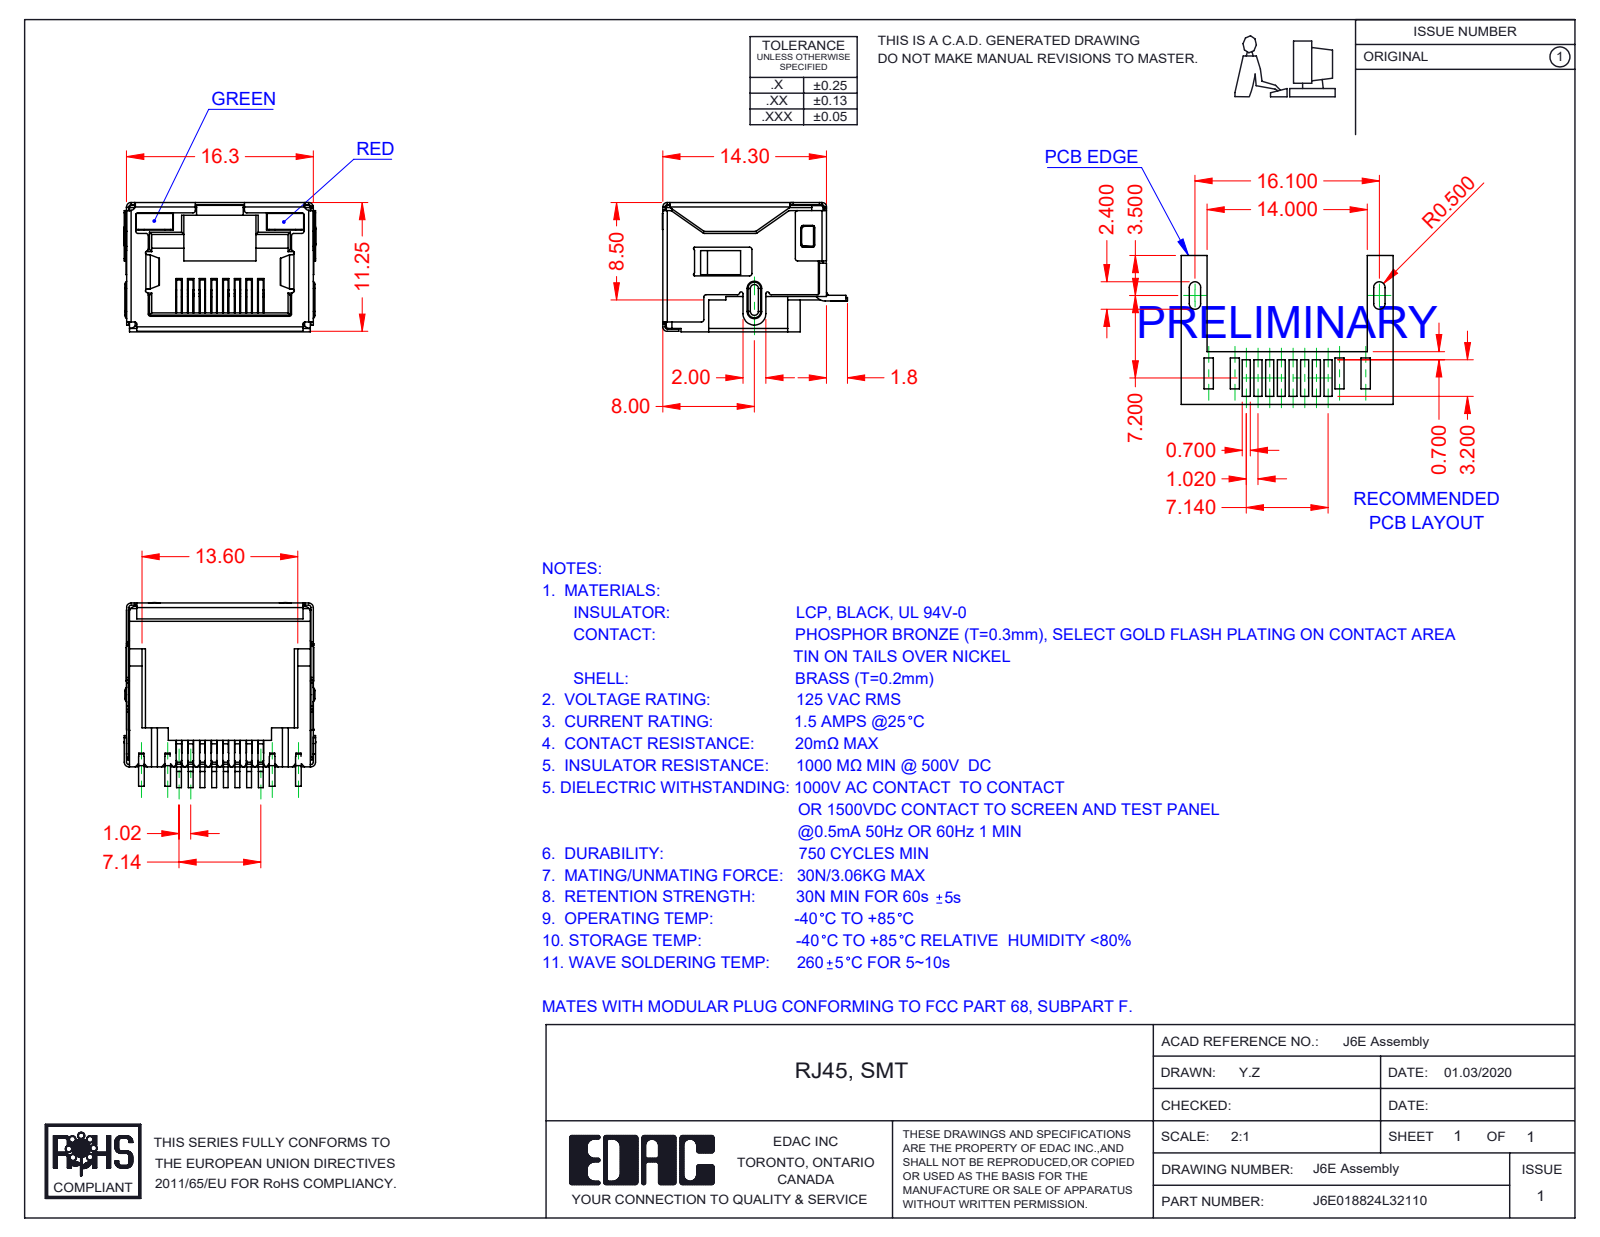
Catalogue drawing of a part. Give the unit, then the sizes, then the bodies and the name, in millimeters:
Units: millimetres
Overall size (bounding box): 16.75 × 16.15 × 11.3
Partial cylindrical surfaces — rounded edges, fillets, slot ends (radius × count): R0.2 ×82, R0.25 ×17, R0.4 ×13, R0.5 ×13, R0.1 ×10, R0.15 ×7, R0.3 ×4, R1 ×3
Main face-to-face distances: 11.05, 16.05, 16.1, 15.85, 11.1, 11.3, 2.4, 0.7, 9.85, 0.49
Volume: 1 109 mm³ · Surface area: 4 045 mm²
Bodies: 12 solids, 1496 faces (1099 planar, 347 cylindrical, 50 other)
Part name (STEP PRODUCT): J6E018824L32110; 6E LED LH_3-Green; 6E Shield_LED; 6E Contacts (+2 more)
STEP written by: SolidWorks 2016 (CONFIG_CONTROL_DESIGN)
